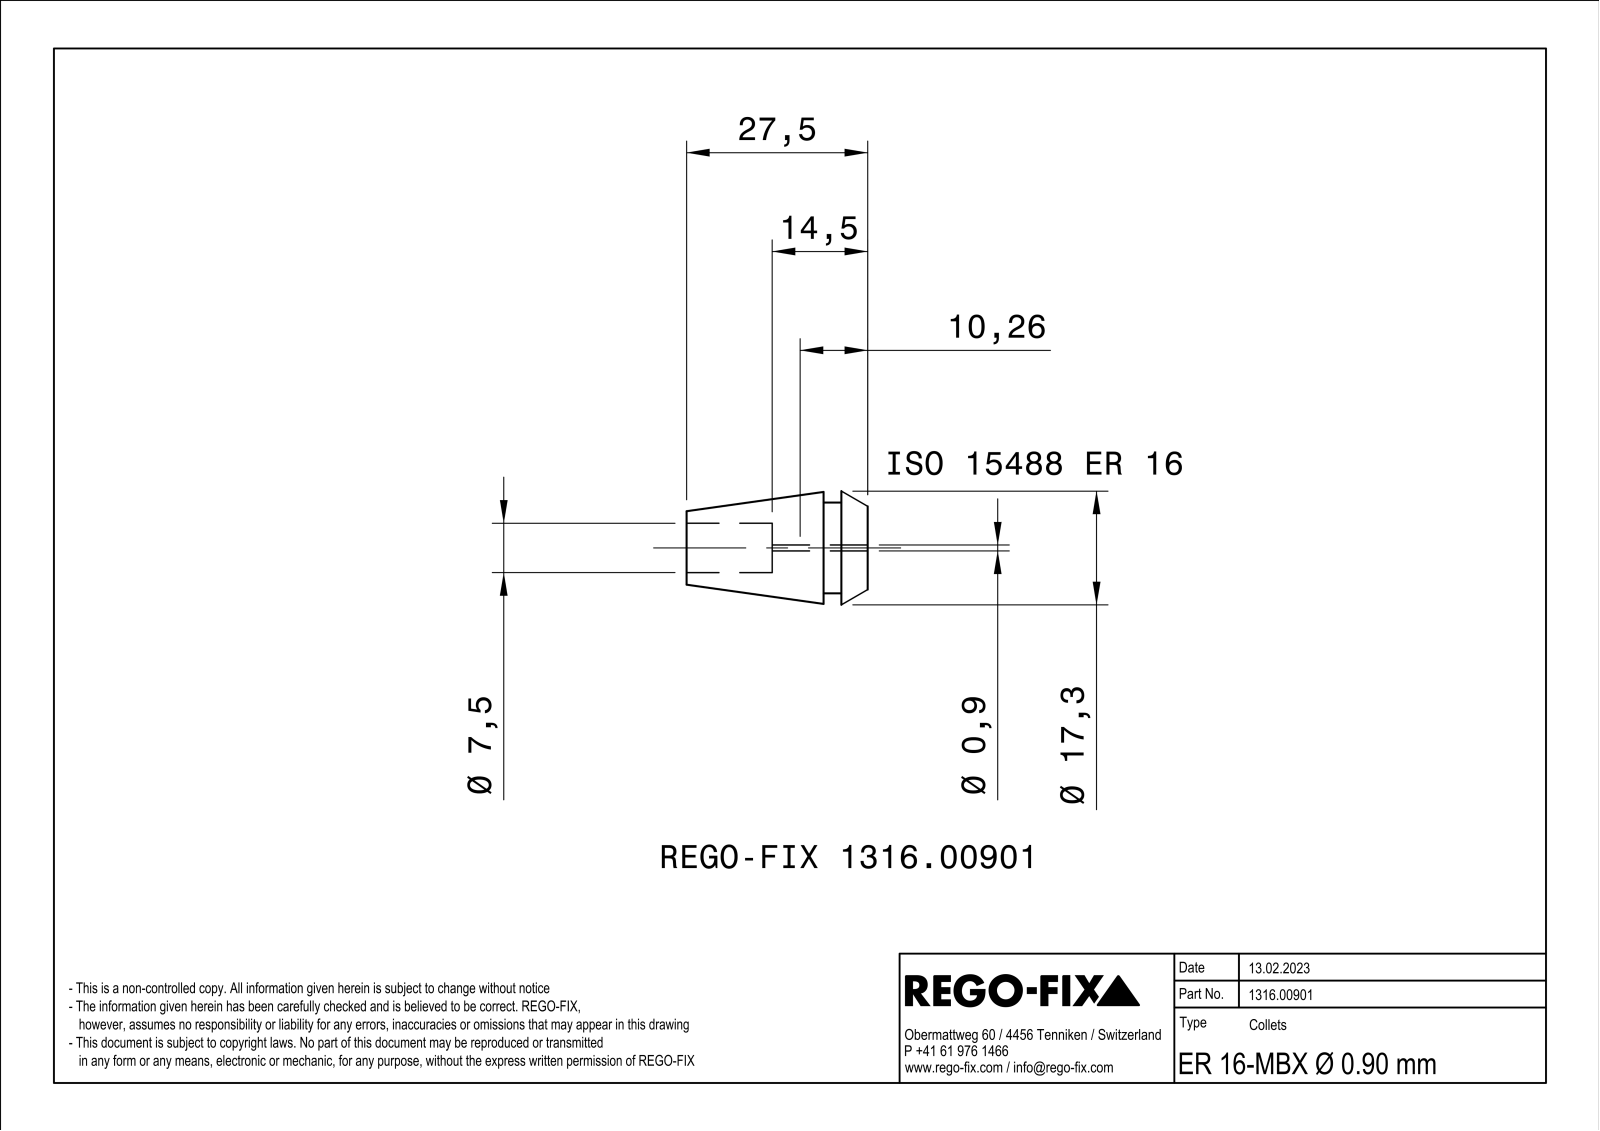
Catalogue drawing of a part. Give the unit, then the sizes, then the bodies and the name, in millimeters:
Units: millimetres
Overall size (bounding box): 27.5 × 16.91 × 16.9
Round holes (diameter × count): ⌀2 ×3, ⌀7.5 ×1
Round bosses / shafts (diameter × count): ⌀13.8 ×1
Partial cylindrical surfaces — rounded edges, fillets, slot ends (radius × count): R0.14 ×3, R25 ×3, R0.45 ×1
Main face-to-face distances: 0.54, 0.8, 6.7, 4, 2.7, 27.5, 23.5, 20.8, 14.5, 10.5
Hole centre spacings: 2.1, 3.64
Volume: 3 300 mm³ · Surface area: 3 318 mm²
Bodies: 1 solid, 109 faces (36 planar, 27 cylindrical, 46 other)
Part name (STEP PRODUCT): NOCUT
STEP written by: SIEMENS PLM Software Solid Edge ST10 (AUTOMOTIVE_DESIGN)
